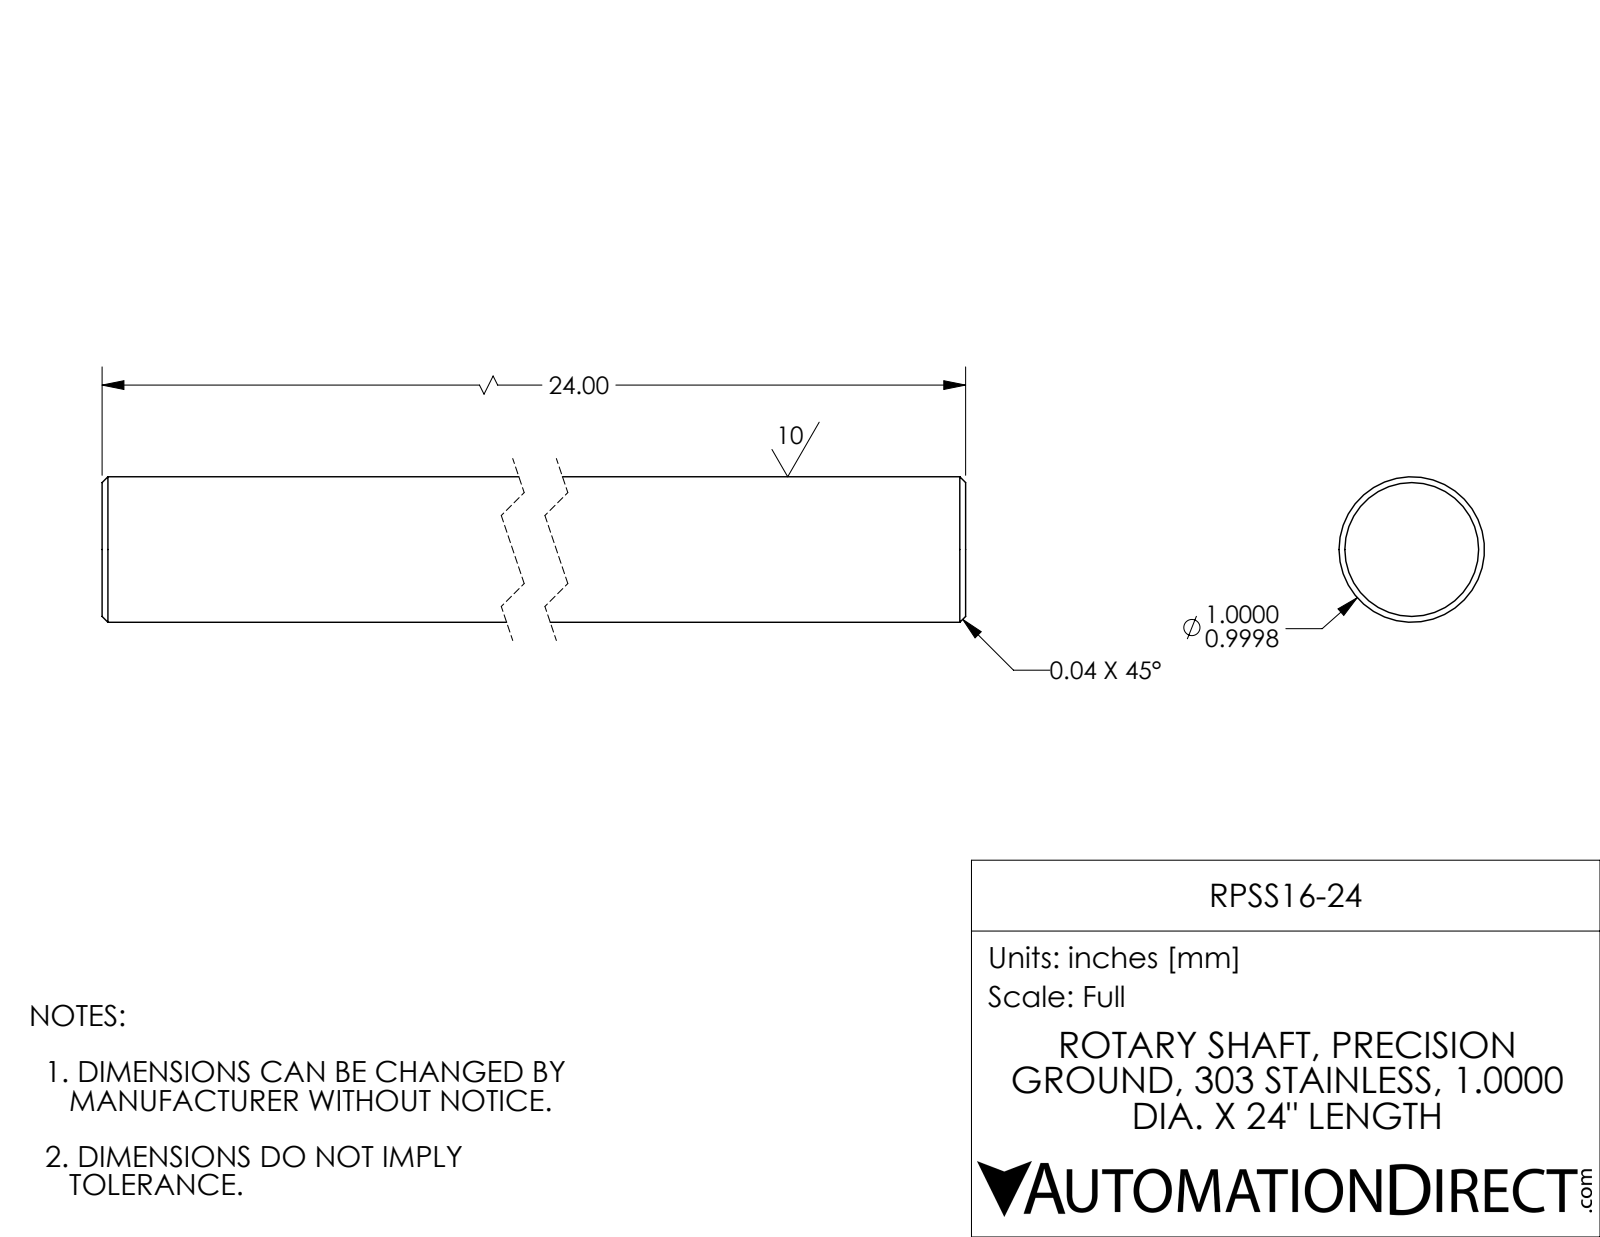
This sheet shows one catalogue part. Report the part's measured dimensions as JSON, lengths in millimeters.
{"part_name": "RPSS16-24", "step_written_by": "SolidWorks 2017 (AUTOMOTIVE_DESIGN)", "units": "millimeters", "bodies": {"solids": 1, "faces": 8, "planar": 2, "cylindrical": 2, "other": 4}, "overall_size": [609.6, 25.4, 25.4], "volume_mm3": 308700, "surface_area_mm2": 49560, "round_bosses_or_shafts": [[25.4, 1]], "face_to_face_distances": [609.6]}
